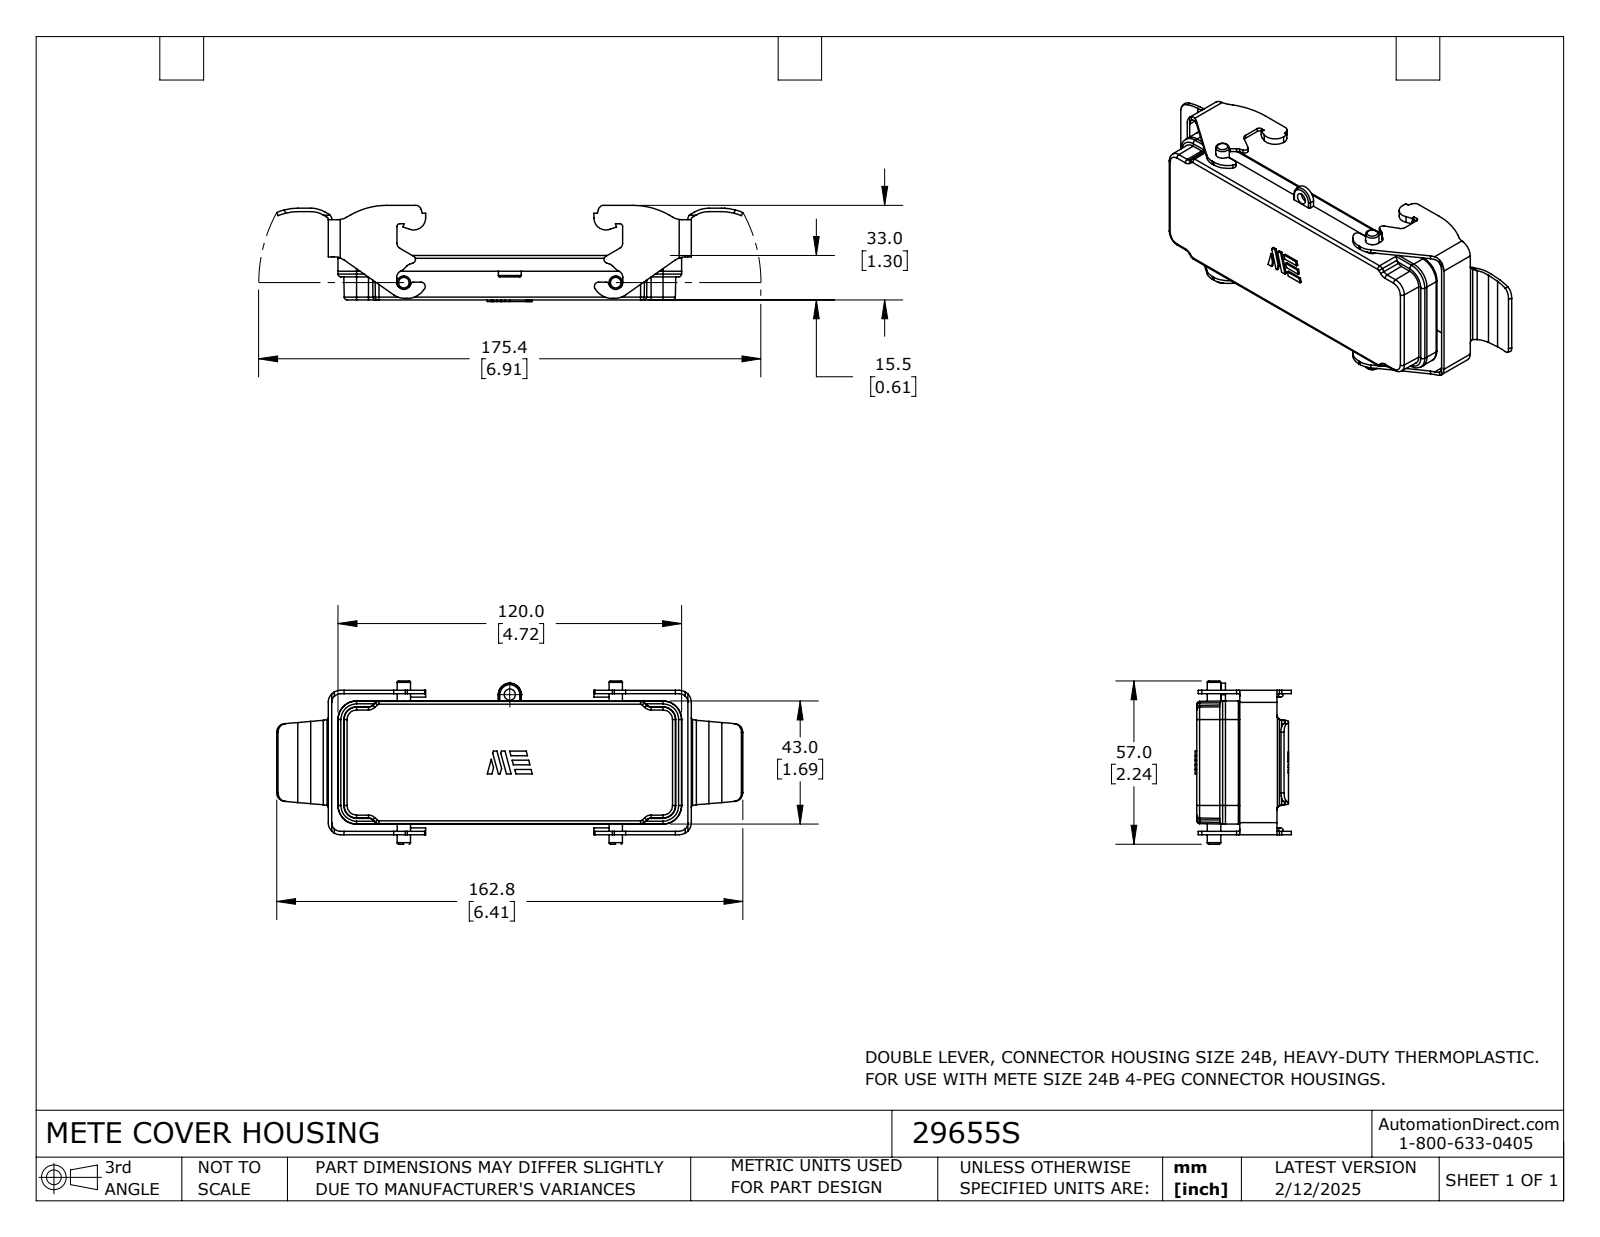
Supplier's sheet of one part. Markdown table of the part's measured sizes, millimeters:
| quantity | value |
| --- | --- |
| part name | 29655S |
| STEP written by | SolidWorks 2024 (CONFIG_CONTROL_DESIGN) |
| units | millimeters |
| bodies | 1 solid, 506 faces (206 planar, 216 cylindrical, 84 other) |
| overall size | 162.8 × 57 × 33.6 |
| volume | 28 150 mm³ |
| surface area | 30 300 mm² |
| round bosses / shafts (diameter × count) | 4.7 × 2 |
| partial cylindrical surfaces (radius × count) | 0.2 × 32, 1 × 32, 0.5 × 14, 3 × 10, 1.5 × 6, 2 × 6, 2.5 × 6, 4.2 × 6 |
| main face-to-face distances | 2, 1.2, 3.7, 49.2, 43, 2.6, 48, 50.4, 125.6, 6.2 |
